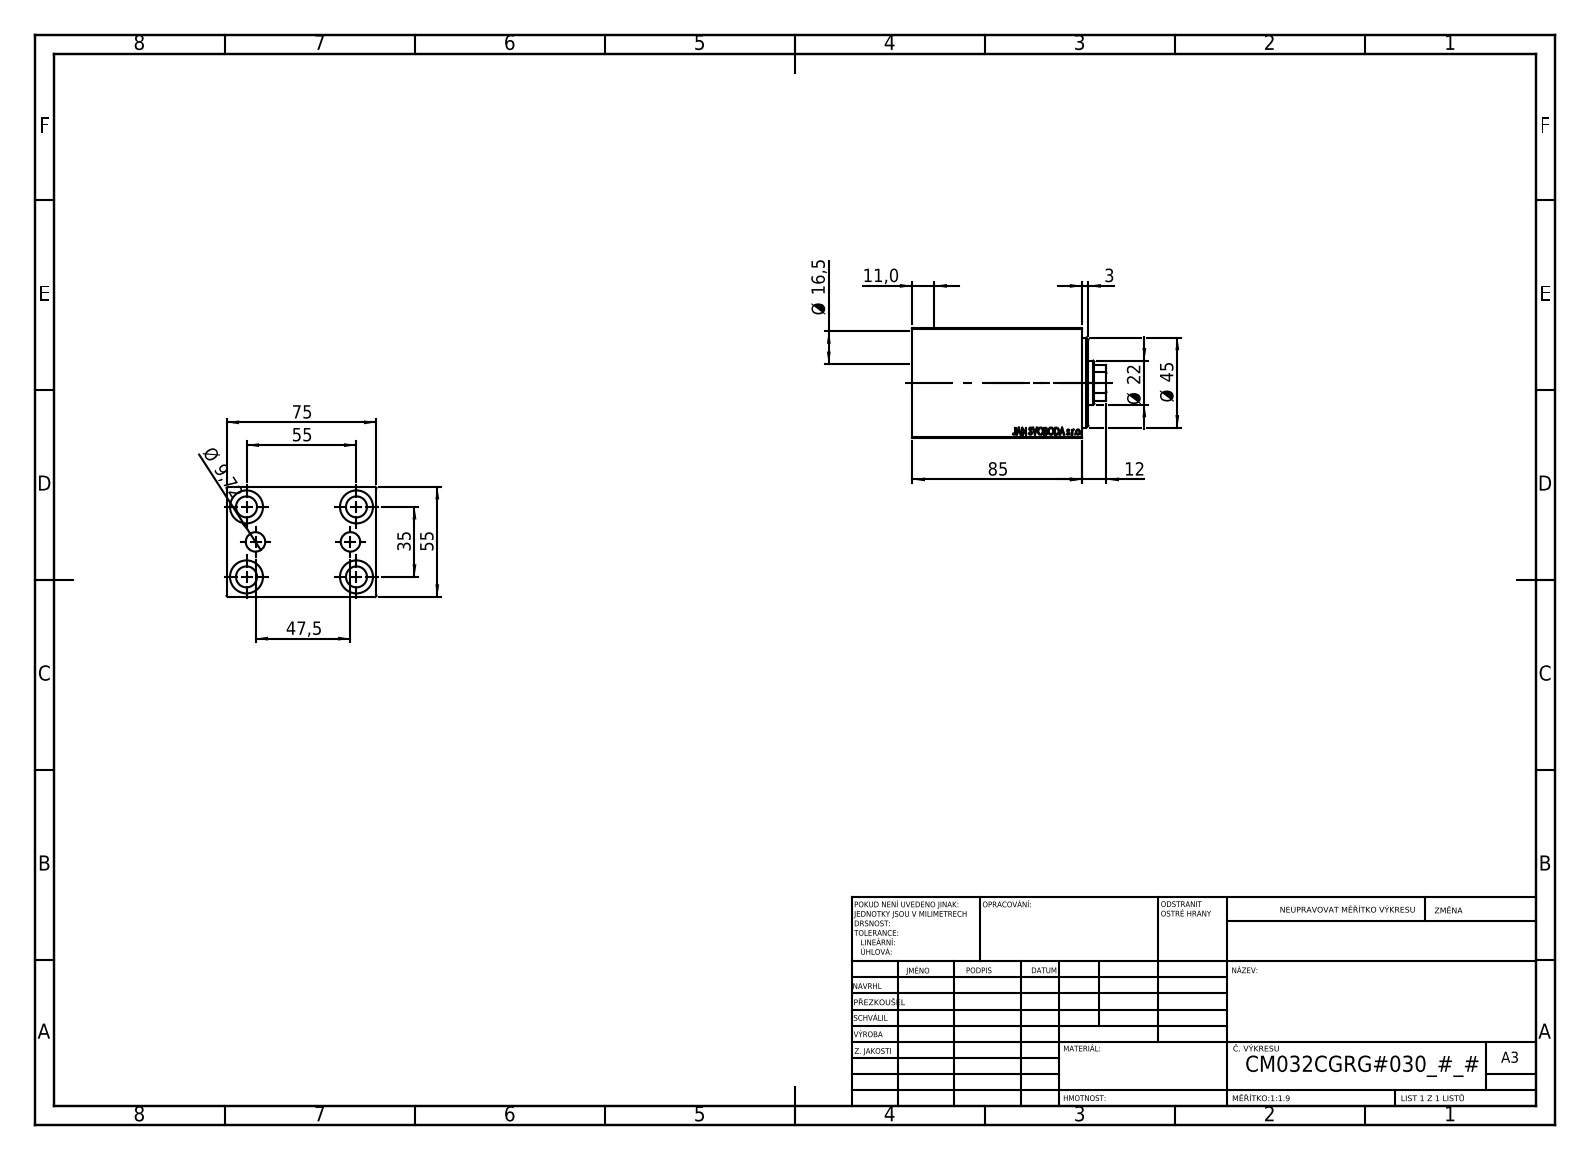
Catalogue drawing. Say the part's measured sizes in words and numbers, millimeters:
The part is named "V450CM_VC_B; V450CM_C_Body; V450CM_C_VCP". Its 3-D file was written by "SolidWorks 2019 (CONFIG_CONTROL_DESIGN)". It is 3 solids with 852 faces: 406 planar, 52 cylindrical and 394 other. Overall it measures 97 by 75 by 55 millimeters. Its volume is 301 531 cubic millimeters and its surface area 65 339 square millimeters. Round holes: 5 of diameter 10.5, 4 of diameter 16.5, 2 of diameter 9.72, 1 of diameter 22, 1 of diameter 25.5, 1 of diameter 32, 1 of diameter 34, 1 of diameter 45. Partial cylindrical surfaces (rounded edges, fillets, slot ends): 1 of radius 10.5. The main face-to-face distances are 55, 75, 10, 85, 80, 5, 70, 63, 11, 74. The hole center spacings are 32.6, 17.76, 18.07, 35, 53.45, 54.87, 55, 65.19.
